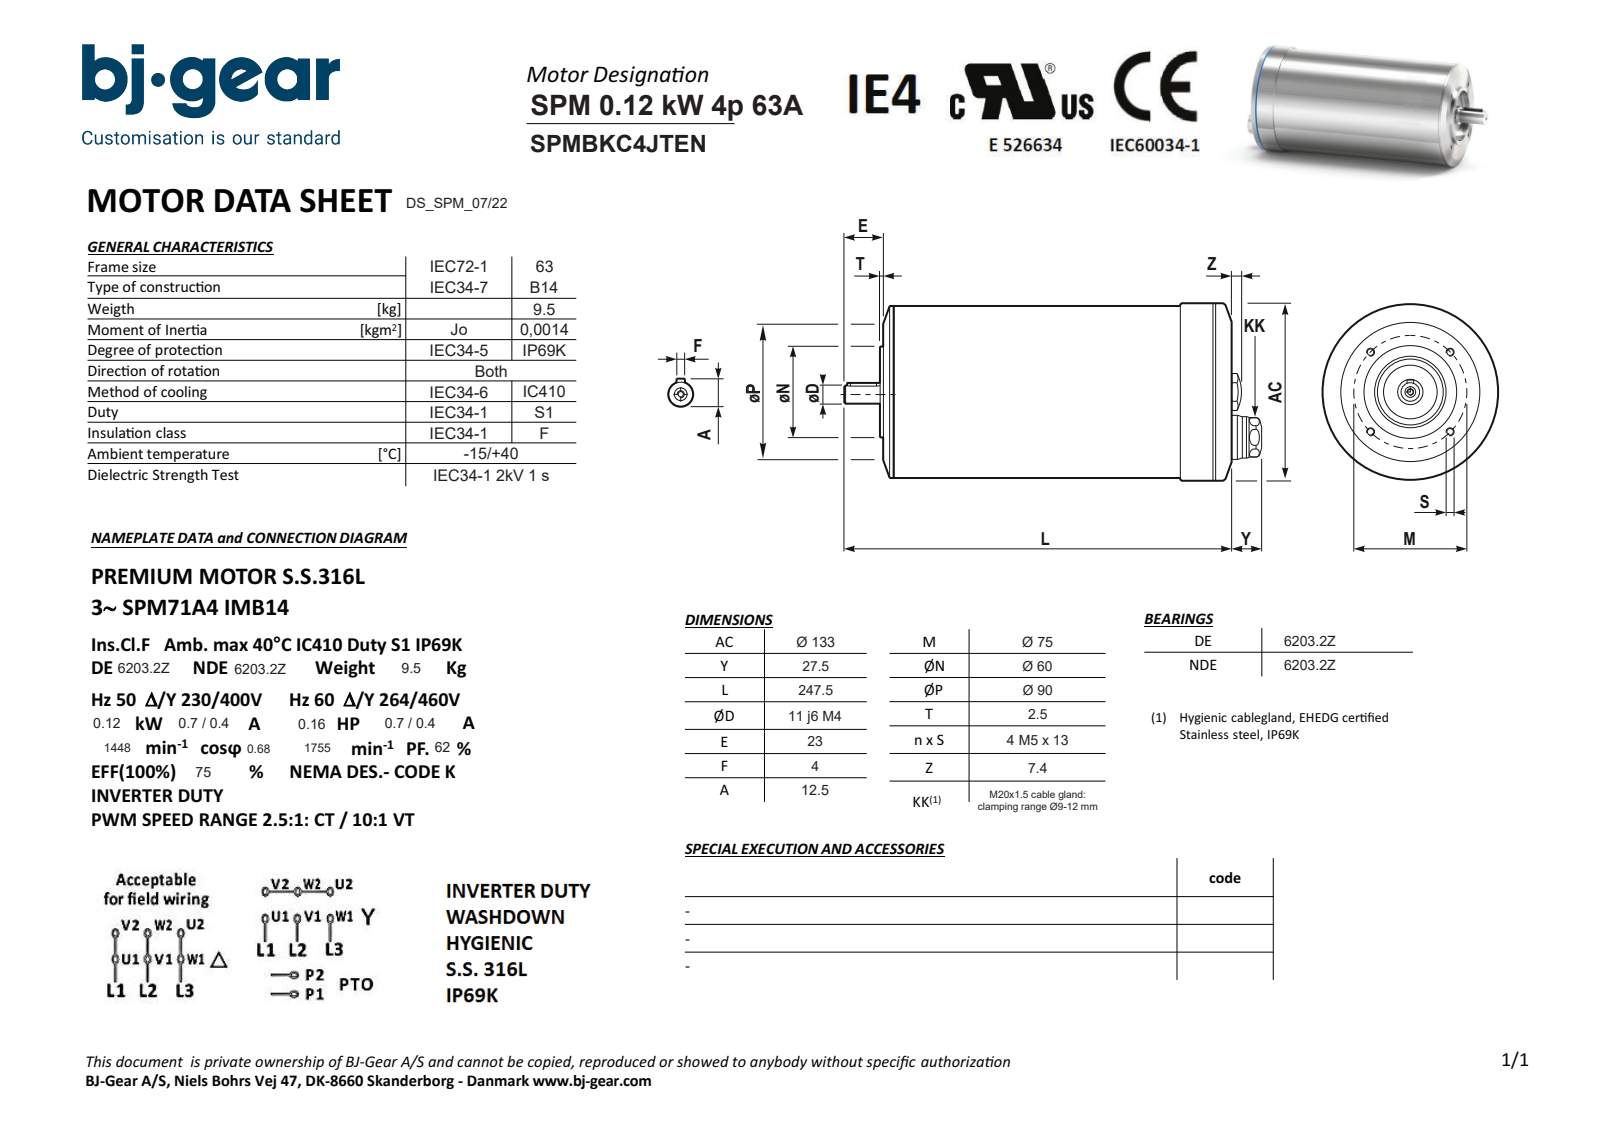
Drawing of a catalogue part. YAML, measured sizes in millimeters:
part_name: "SPMBKC4JTENN4KSA1-N---NNN"
step_written_by: "Solid Edge (AUTOMOTIVE_DESIGN)"
units: millimeters
bodies: {solids: 1, faces: 87, planar: 30, cylindrical: 32, other: 25}
overall_size: [275, 133, 133]
volume: 2939000
surface_area: 120931
round_holes:
  - {diameter: 4.13, count: 4}
  - {diameter: 3.24, count: 1}
  - {diameter: 4.3, count: 1}
  - {diameter: 7, count: 1}
  - {diameter: 13.4, count: 1}
  - {diameter: 52, count: 1}
round_bosses_or_shafts:
  - {diameter: 133, count: 1}
  - {diameter: 132.98, count: 1}
  - {diameter: 129, count: 1}
  - {diameter: 128.98, count: 1}
  - {diameter: 60, count: 1}
  - {diameter: 20, count: 1}
  - {diameter: 17, count: 1}
  - {diameter: 11, count: 1}
partial_cylinders:
  - {radius: 2, count: 2}
  - {radius: 12.8, count: 1}
face_to_face_distances: [224.5, 219, 5.5, 2.5, 8, 227, 24, 12, 231, 236.5]
hole_center_spacings: [37.5, 53.04, 27.55, 66.08, 75.01, 34]
